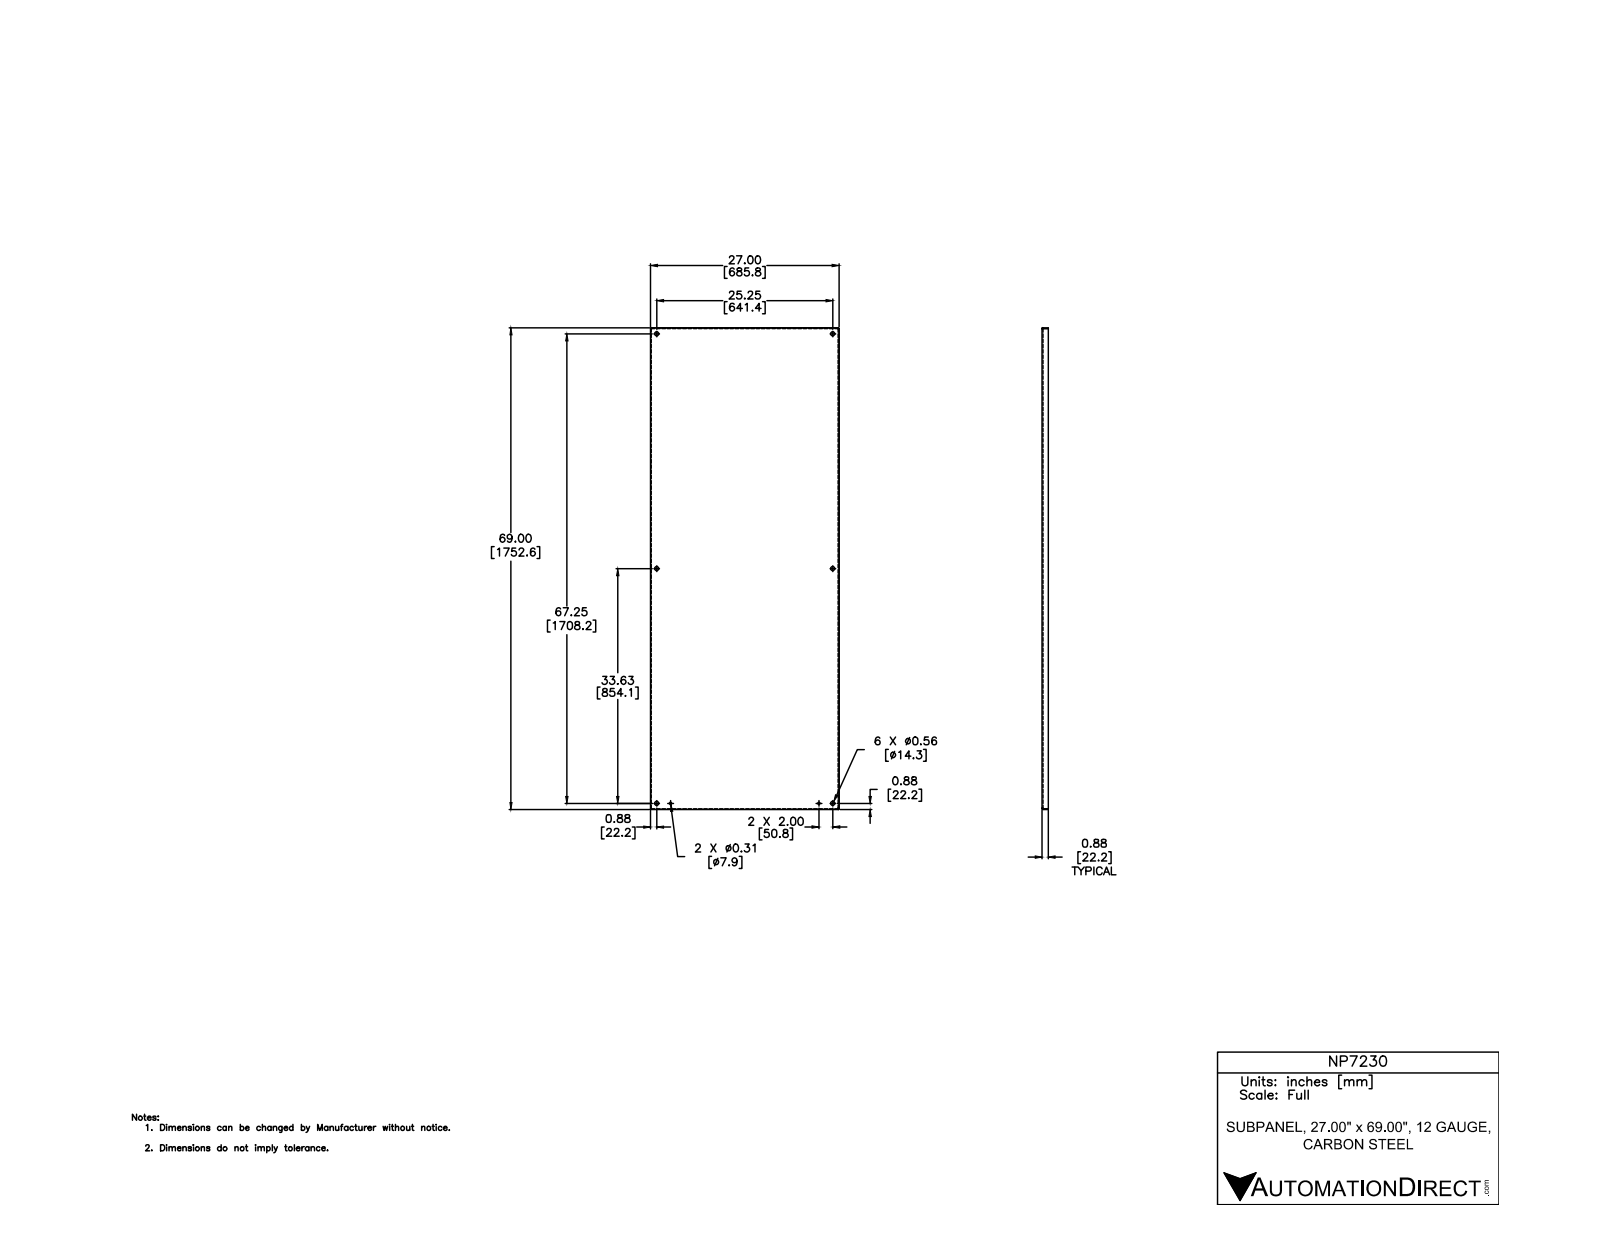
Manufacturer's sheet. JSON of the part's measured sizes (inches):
{"part_name": "NP7230", "step_written_by": "Autodesk Inventor 2012 (AUTOMOTIVE_DESIGN)", "units": "inches", "bodies": {"solids": 1, "faces": 46, "planar": 22, "cylindrical": 16, "other": 8}, "overall_size": [69, 27, 0.875], "volume_in3": 187.9, "surface_area_in2": 4028, "round_holes": [[0.563, 6], [0.312, 2]], "partial_cylinders_radius": [[0.031, 4], [0.125, 4]], "face_to_face_distances": [0.094, 26.906, 27, 26.813, 68.906, 69, 68.813, 0.781, 0.875, 0.105], "hole_center_spacings": [33.625, 25.25, 33.685, 40.881, 42.05, 42.05, 67.25, 71.834]}
